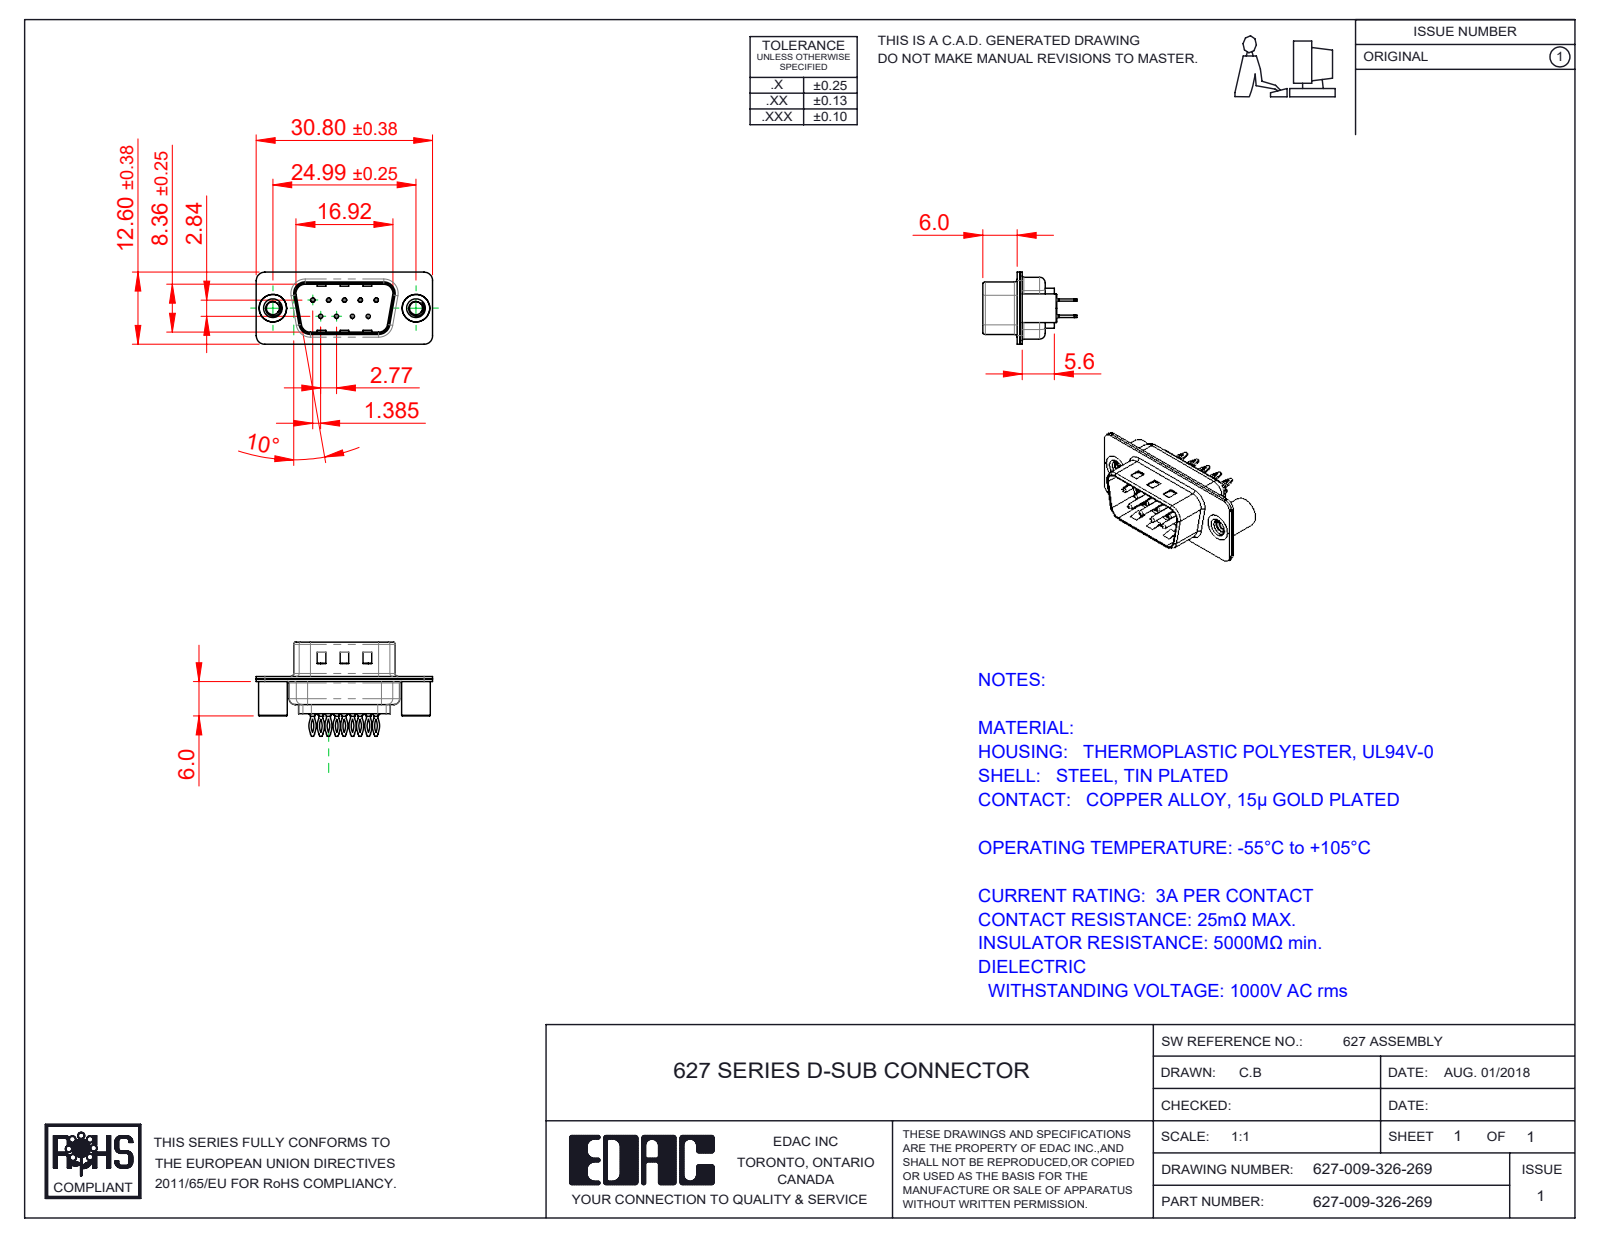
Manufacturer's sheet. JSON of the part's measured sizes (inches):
{"part_name": "627 Contact Row 1_26L; 627 4-40 Threaded Standoff BS; 627-009-326-069; 627 Shell Front_09 Contacts (+3 more)", "step_written_by": "SolidWorks 2020 (CONFIG_CONTROL_DESIGN)", "units": "inches", "bodies": {"solids": 14, "faces": 1010, "planar": 287, "cylindrical": 428, "other": 295}, "overall_size": [1.213, 0.648, 0.496], "volume_in3": 0.086, "surface_area_in2": 6.349, "round_holes": [[0.014, 9], [0.043, 9], [0.063, 9], [0.089, 2], [0.157, 2], [0.189, 2]], "round_bosses_or_shafts": [[0.079, 9], [0.059, 9], [0.03, 9], [0.197, 2], [0.193, 2]], "partial_cylinders_radius": [[0.059, 18], [0.115, 18], [0.131, 18], [0.079, 12], [0.02, 8], [0.063, 8], [0.01, 4], [0.024, 4]], "face_to_face_distances": [0.016, 0.018, 0.035, 0.032, 0.377, 0.055, 0.345, 0.256, 0.02, 0.059], "hole_center_spacings": [0.124, 0.109, 0.218, 0.198, 0.198, 0.327, 0.294, 0.295]}
